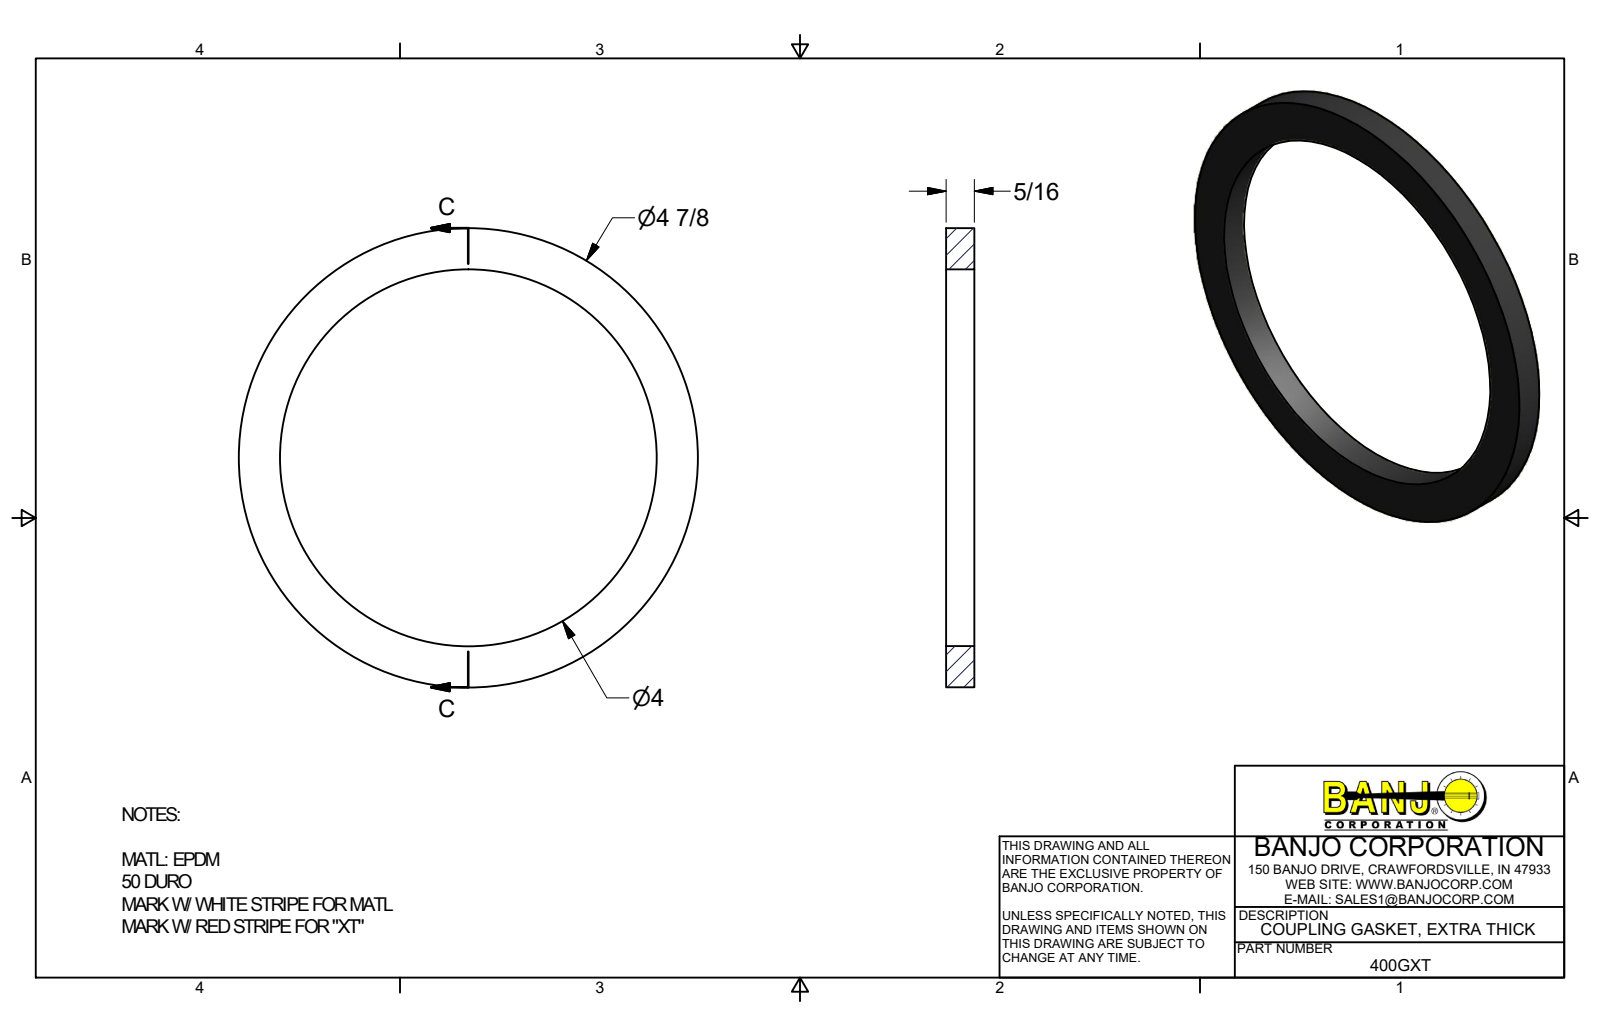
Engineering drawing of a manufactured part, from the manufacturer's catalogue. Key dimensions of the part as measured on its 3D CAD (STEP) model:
Part name (STEP PRODUCT): 400GXT
STEP written by: Autodesk Inventor 2017 (AUTOMOTIVE_DESIGN)
Units: millimetres
Bodies: 1 solid, 4 faces (2 planar, 2 cylindrical, 0 other)
Overall size (bounding box): 123.83 × 123.83 × 7.62
Volume: 29 984 mm³ · Surface area: 13 266 mm²
Round holes (diameter × count): ⌀101.6 ×1
Round bosses / shafts (diameter × count): ⌀123.82 ×1
Main face-to-face distances: 7.62
